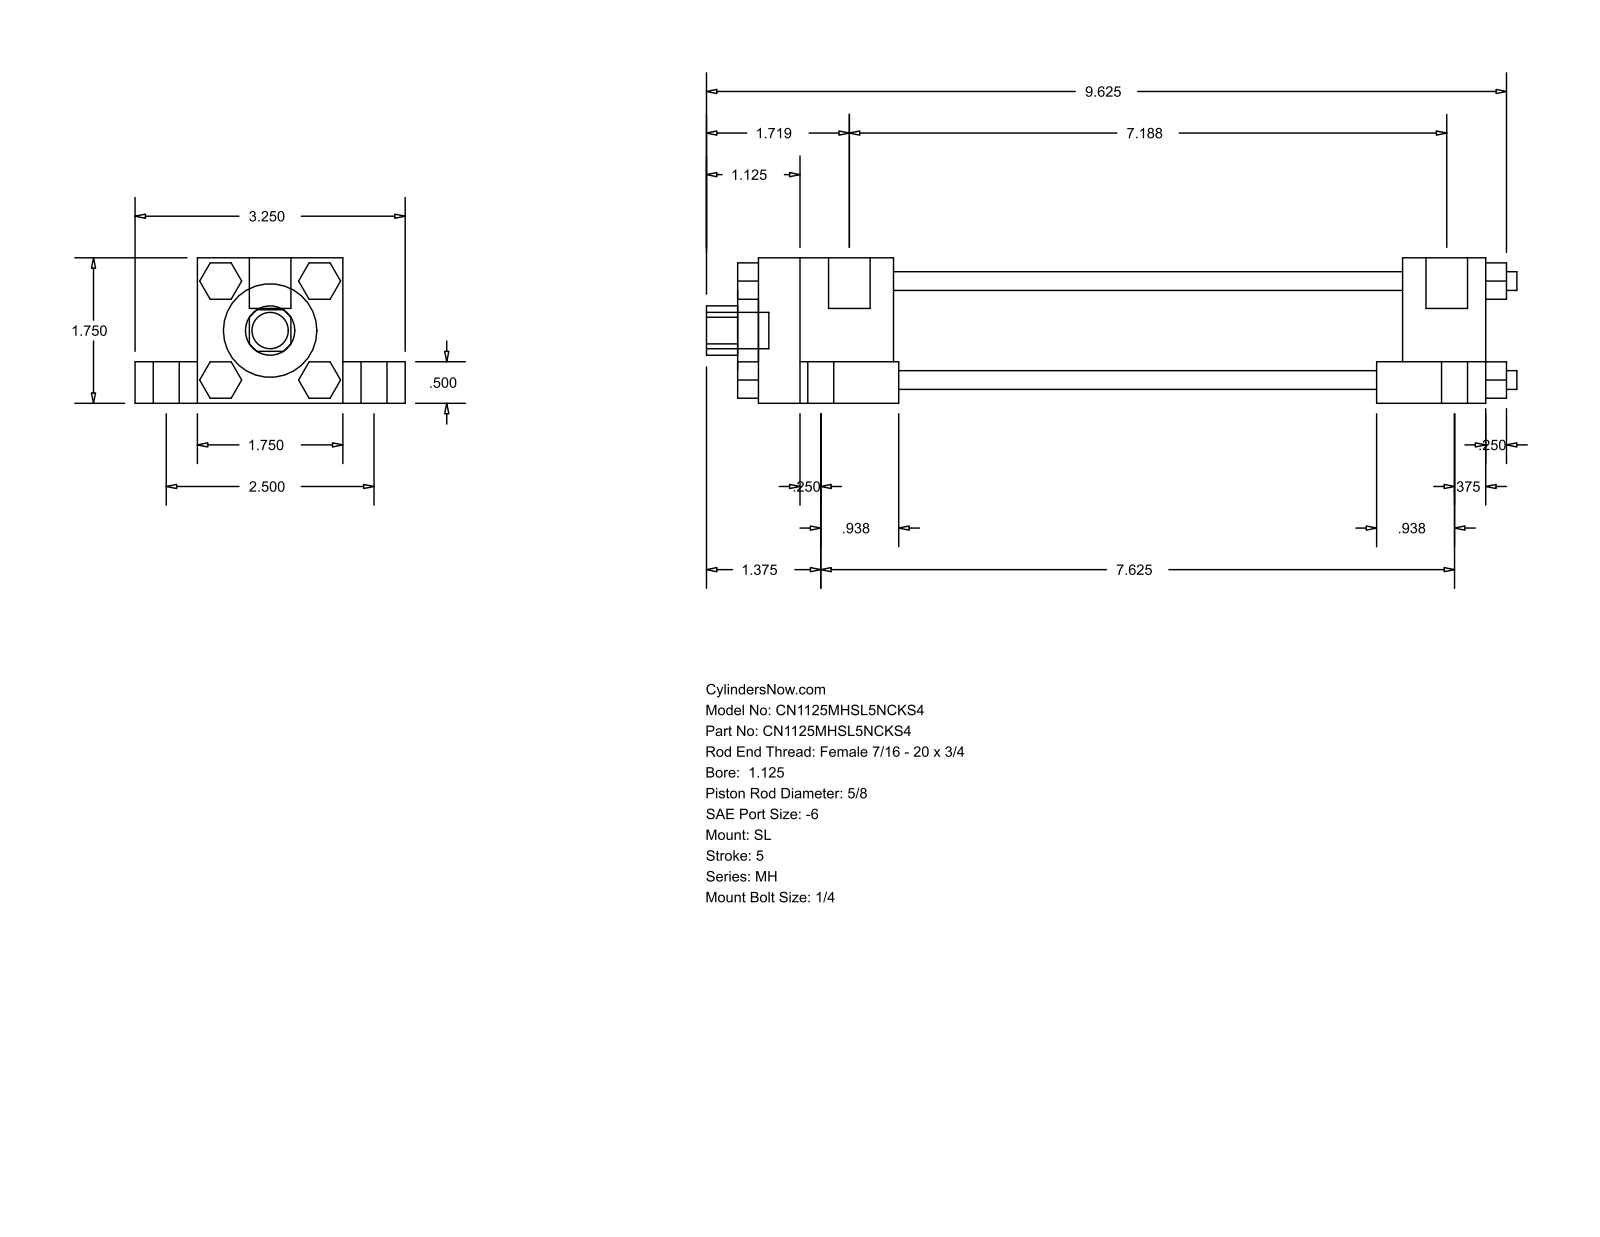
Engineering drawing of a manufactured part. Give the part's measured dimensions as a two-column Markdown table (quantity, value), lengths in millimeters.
| quantity | value |
| --- | --- |
| part name | MH_SL__0112_0.625 |
| STEP written by | GSSL Pune (CONFIG_CONTROL_DESIGN) |
| units | millimeters |
| bodies | 0 solids, 150 faces (114 planar, 36 cylindrical, 0 other) |
| overall size | 247.65 × 82.55 × 44.45 |
| round holes (diameter × count) | 15.88 × 1, 28.57 × 1, 34.92 × 1 |
| round bosses / shafts (diameter × count) | 14.29 × 4, 7.94 × 4, 5.71 × 4, 5.56 × 4, 12.7 × 2, 11.11 × 1 |
| partial cylindrical surfaces (radius × count) | 7.54 × 1 |
| main face-to-face distances | 44.46, 19.04, 12.7, 31.76, 63.5, 6.35, 228.59, 11.11, 155.57, 180.97 |
